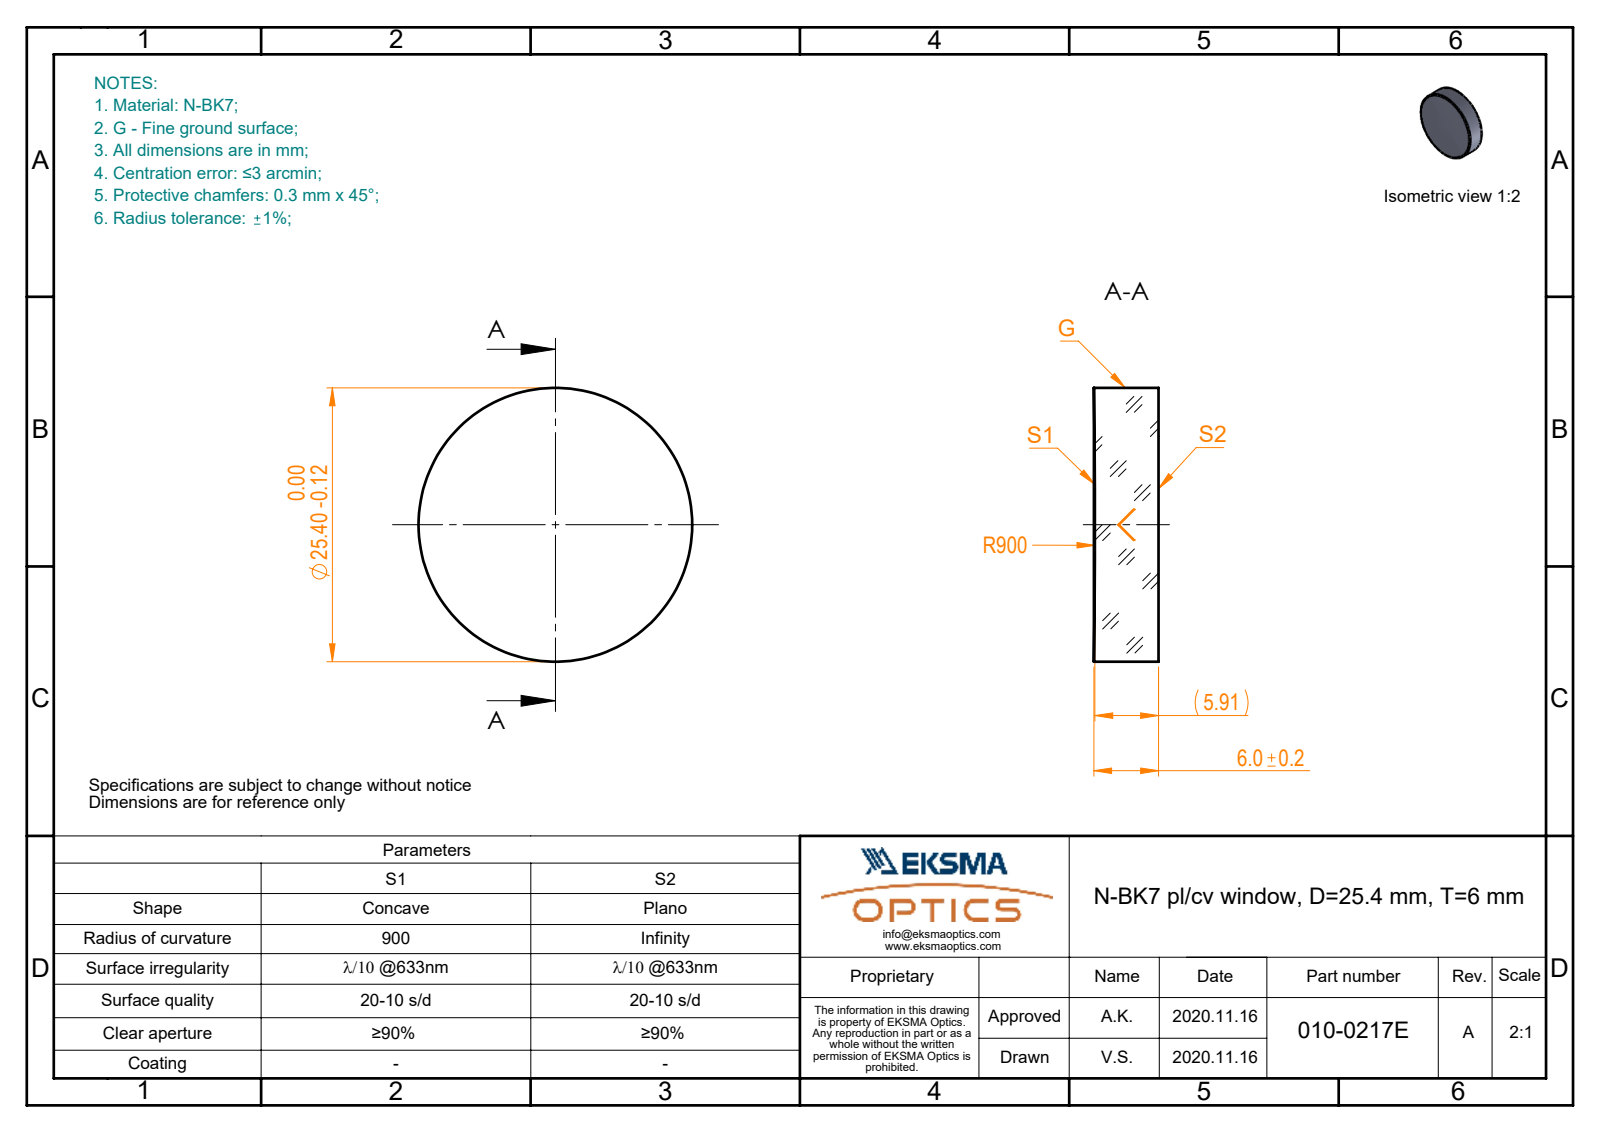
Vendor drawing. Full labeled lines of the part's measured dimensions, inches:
Part name (STEP PRODUCT): 010-0217E_N-BK7_PCV_window
STEP written by: SolidWorks 2019 (CONFIG_CONTROL_DESIGN)
Units: inches
Bodies: 1 solid, 5 faces (1 planar, 2 cylindrical, 2 other)
Overall size (bounding box): 1 × 1 × 0.236
Volume: 0.184 in³ · Surface area: 2.313 in²
Round bosses / shafts (diameter × count): ⌀1 ×1
